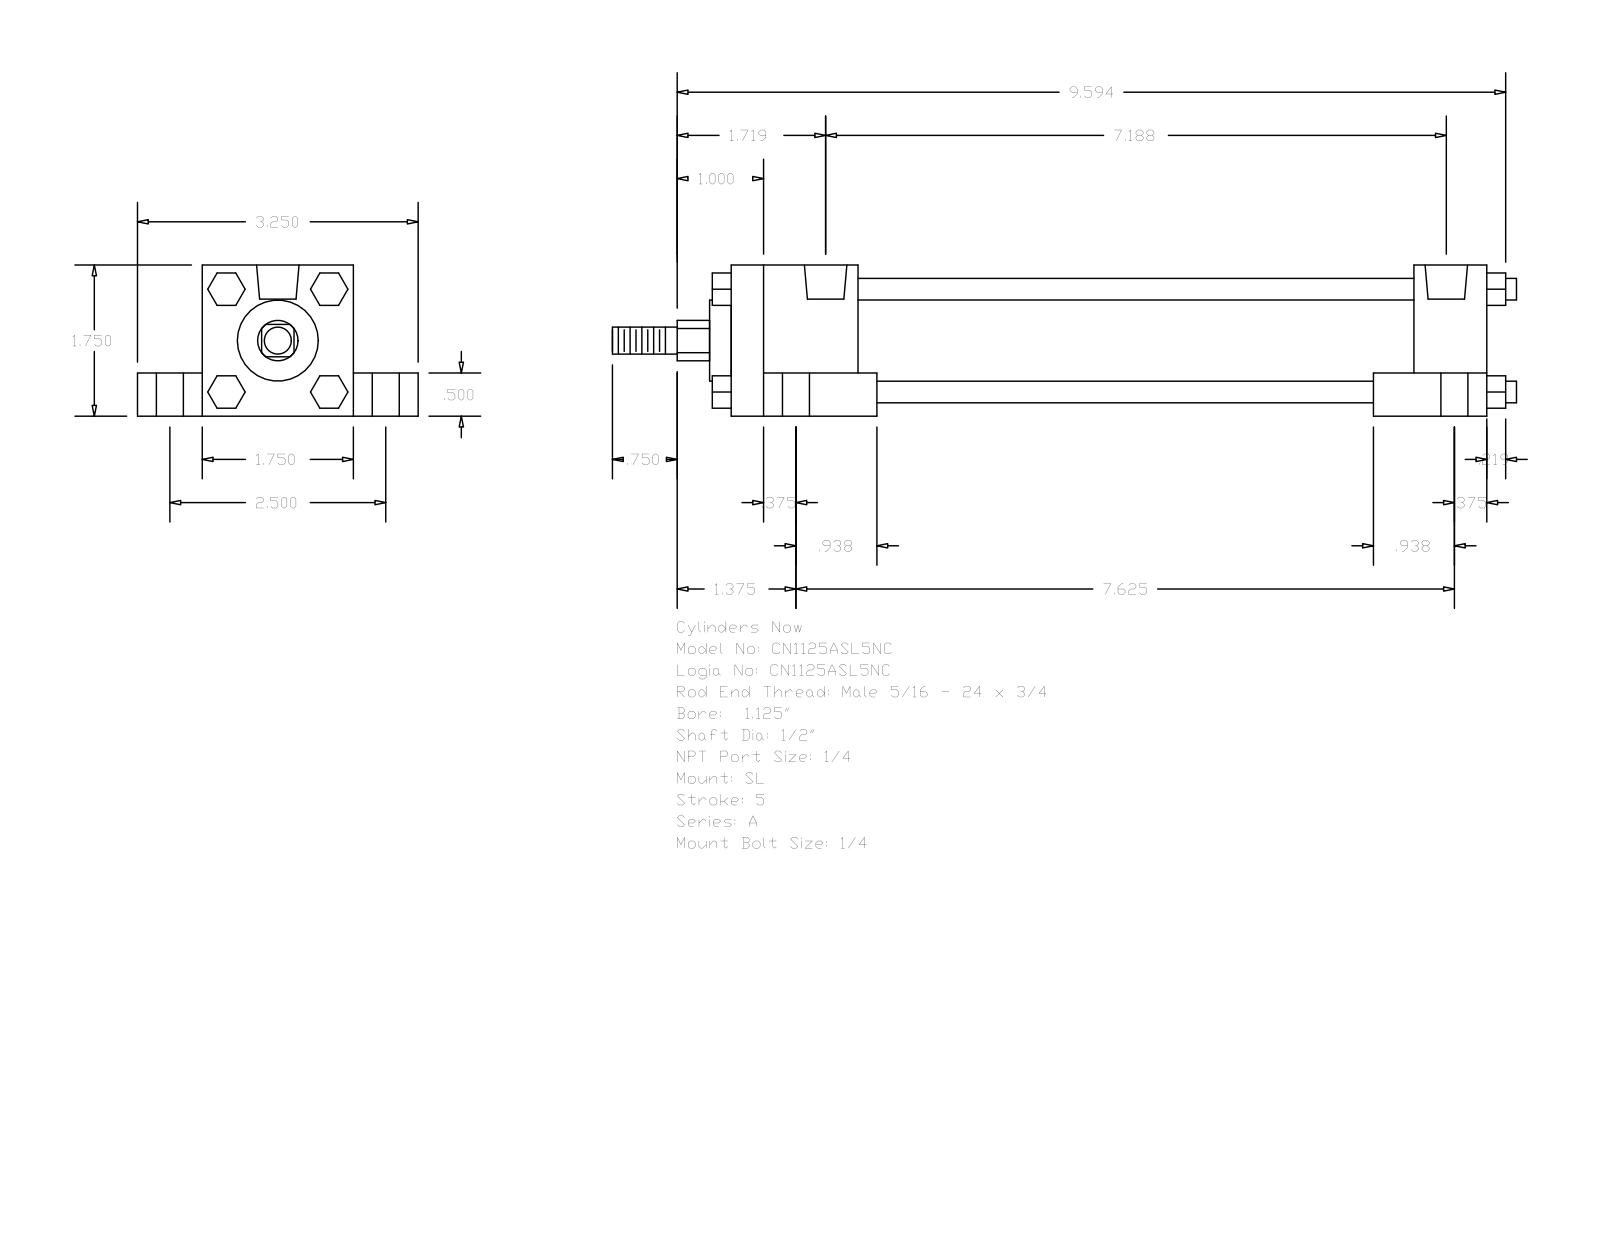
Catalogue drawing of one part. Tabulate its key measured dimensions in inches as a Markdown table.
| quantity | value |
| --- | --- |
| part name | A_SL__0112_0.5 |
| STEP written by | GSSL Pune (CONFIG_CONTROL_DESIGN) |
| units | inches |
| bodies | 0 solids, 150 faces (114 planar, 36 cylindrical, 0 other) |
| overall size | 10.469 × 3.25 × 1.75 |
| round holes (diameter × count) | 0.219 × 4, 0.313 × 4, 0.563 × 4, 0.492 × 2 |
| round bosses / shafts (diameter × count) | 0.25 × 4, 1.255 × 1, 0.937 × 1, 0.5 × 1, 0.313 × 1 |
| partial cylindrical surfaces (radius × count) | 0.234 × 1 |
| main face-to-face distances | 1.75, 1.25, 0.5, 0.75, 2.5, 7.281, 8.75, 7.906, 0.844, 1.469 |
| hole center spacings | 1.254, 1.26, 1.296, 1.315, 2.5, 7.063, 7.326, 7.388 |
